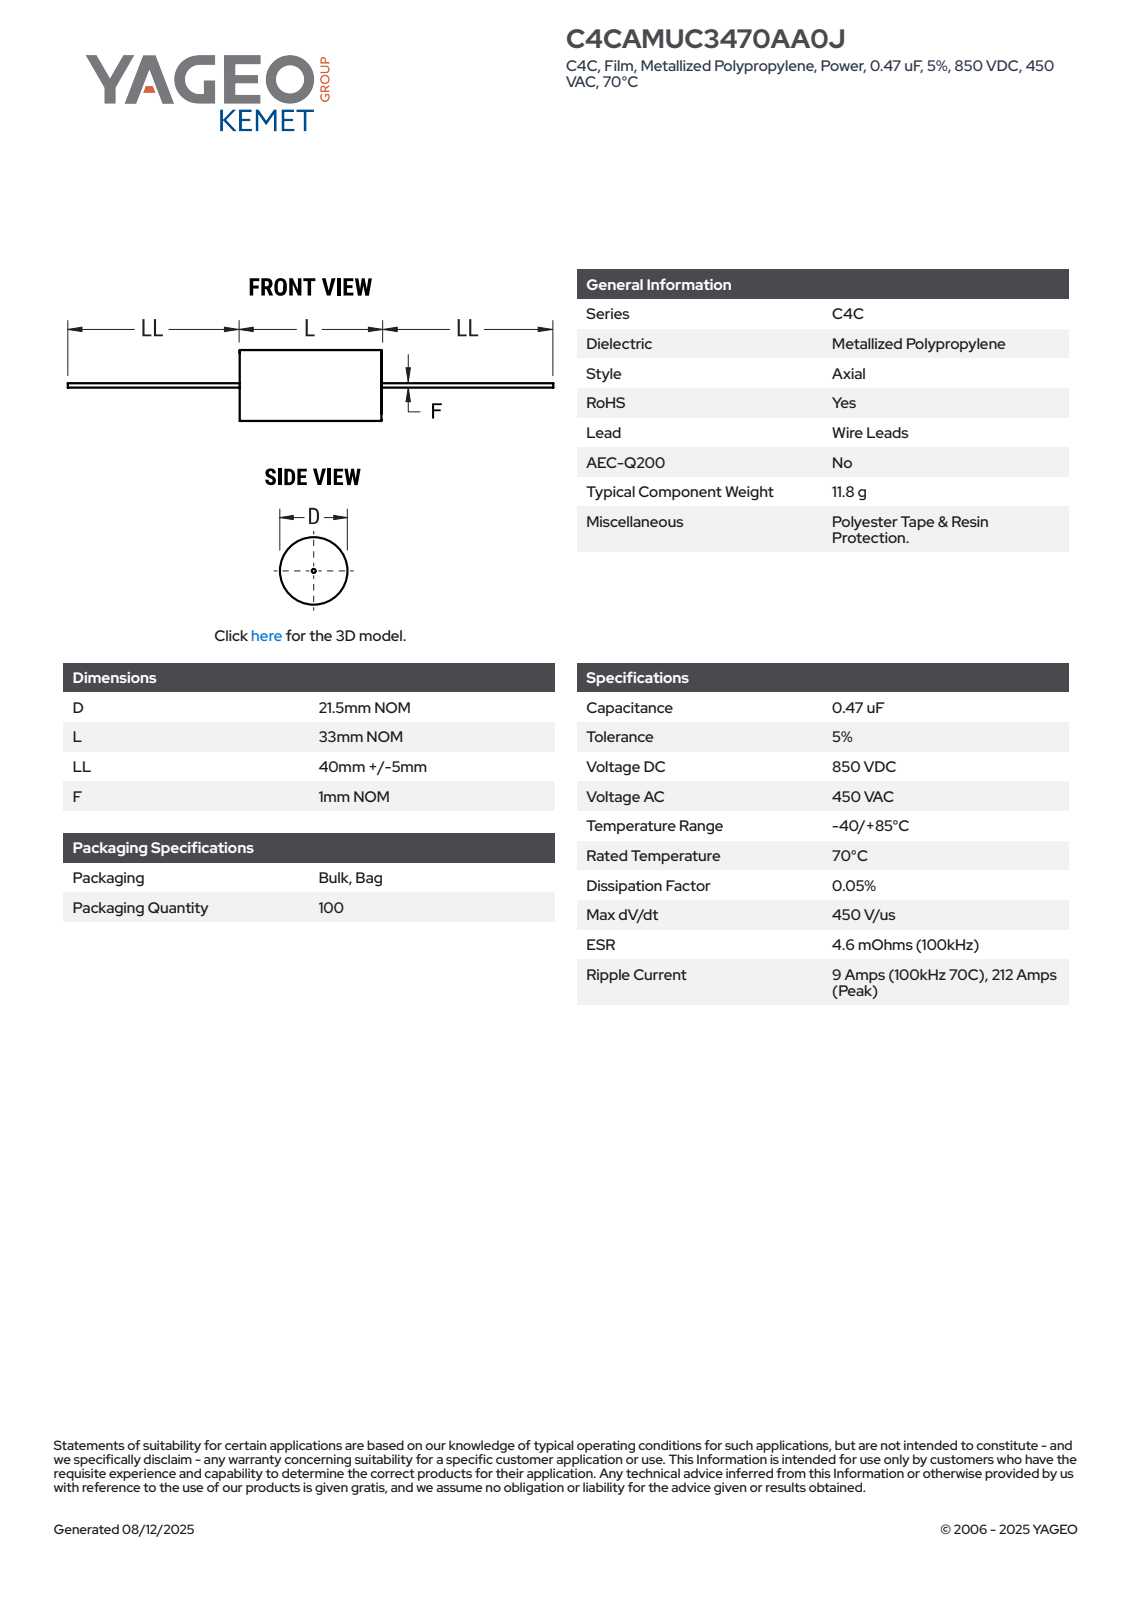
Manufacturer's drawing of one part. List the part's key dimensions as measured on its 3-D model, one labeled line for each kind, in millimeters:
Part name (STEP PRODUCT): CFP_ACWF_21.5X33_D21.5L33LL45F1
STEP written by: SolidWorks 2014 (AUTOMOTIVE_DESIGN)
Units: millimetres
Bodies: 2 solids, 87 faces (28 planar, 28 cylindrical, 31 other)
Overall size (bounding box): 123 × 21.5 × 21.5
Volume: 12 051 mm³ · Surface area: 3 963 mm²
Round bosses / shafts (diameter × count): ⌀21.5 ×1, ⌀1 ×1
Partial cylindrical surfaces — rounded edges, fillets, slot ends (radius × count): R10.74 ×1
Main face-to-face distances: 33.01, 33, 45, 78, 44.99, 123, 78.01
